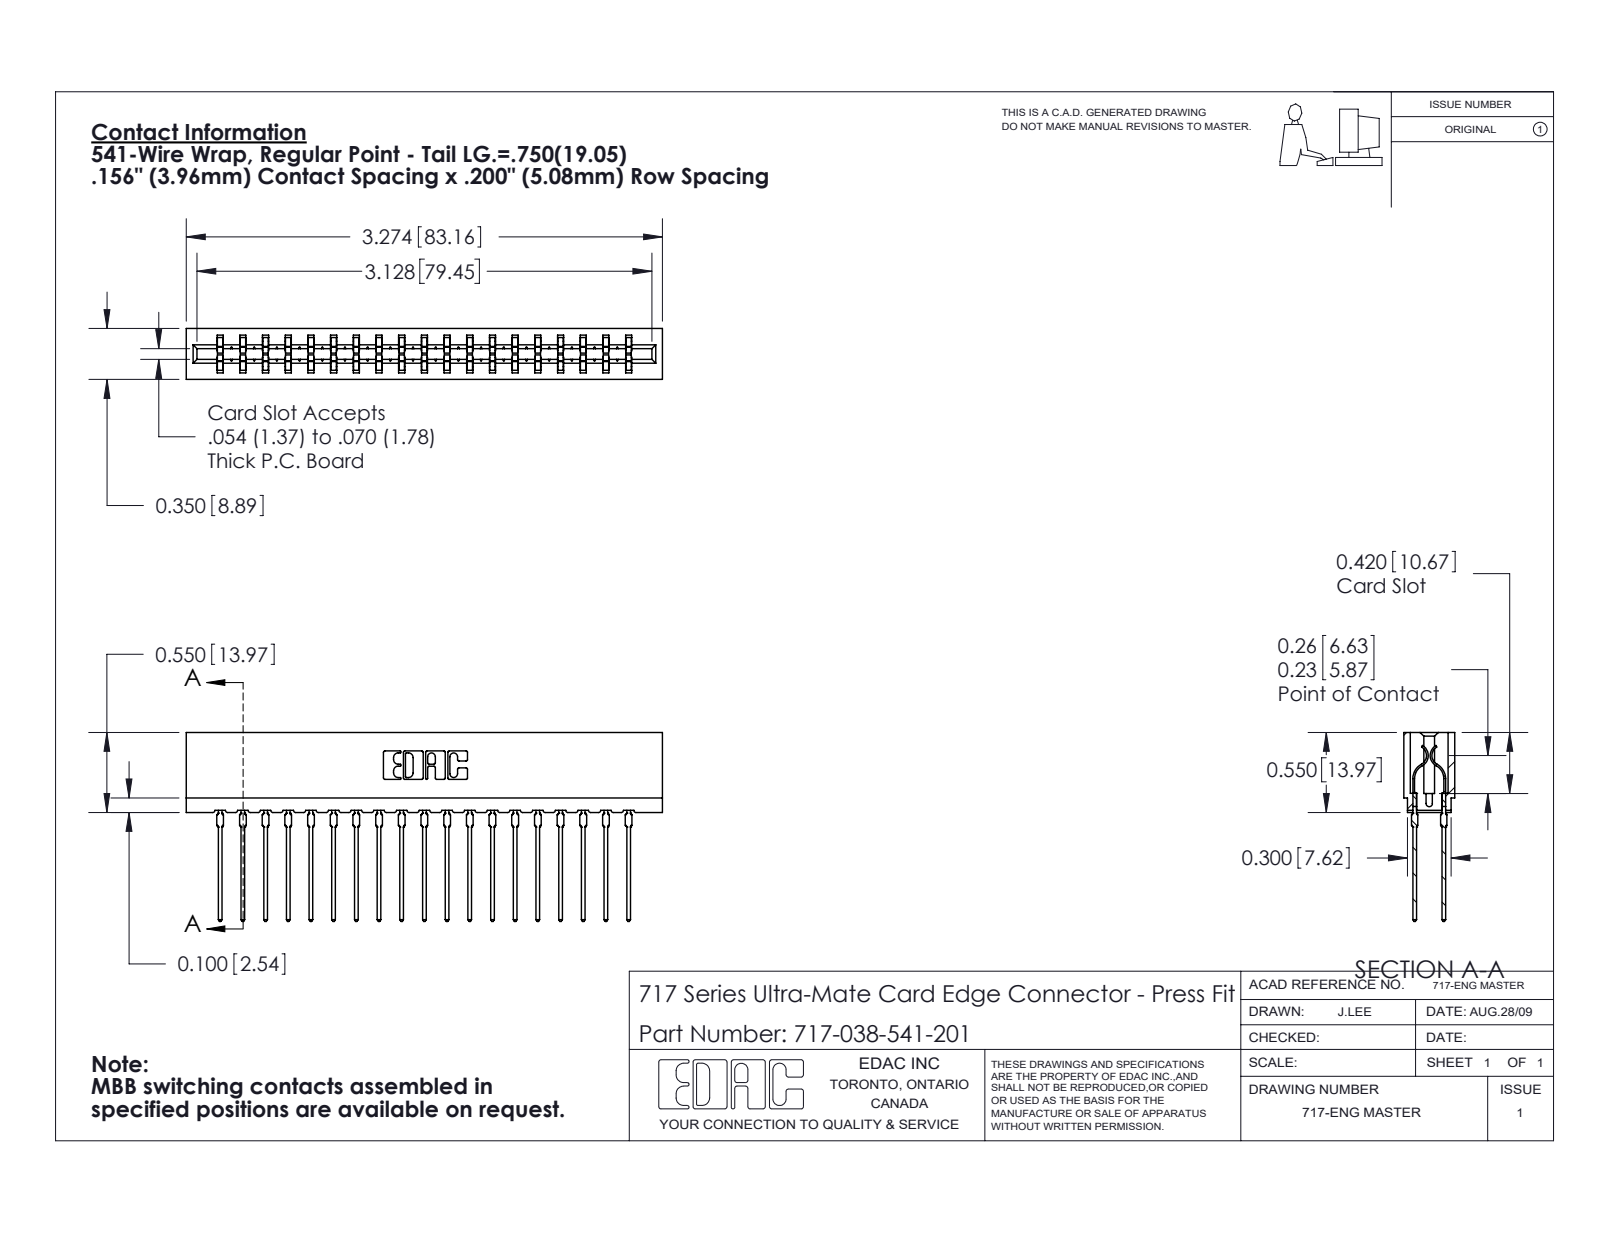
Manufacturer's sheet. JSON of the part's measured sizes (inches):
{"part_name": "717 Part_Insulator Option - 06; 745-292-001_541; 717-038-541-201", "step_written_by": "SolidWorks 2020 (CONFIG_CONTROL_DESIGN)", "units": "inches", "bodies": {"solids": 39, "faces": 3514, "planar": 1821, "cylindrical": 705, "other": 988}, "overall_size": [3.274, 1.299, 0.35], "volume_in3": 0.457, "surface_area_in2": 18.59, "partial_cylinders_radius": [[0.021, 76], [0.015, 38], [0.01, 22], [0.005, 8], [0.011, 8], [0.007, 6], [0.031, 6], [0.026, 3]], "face_to_face_distances": [0.212, 0.138, 0.35, 0.063, 0.287, 0.076, 0.149, 0.156, 0.087, 0.263]}
